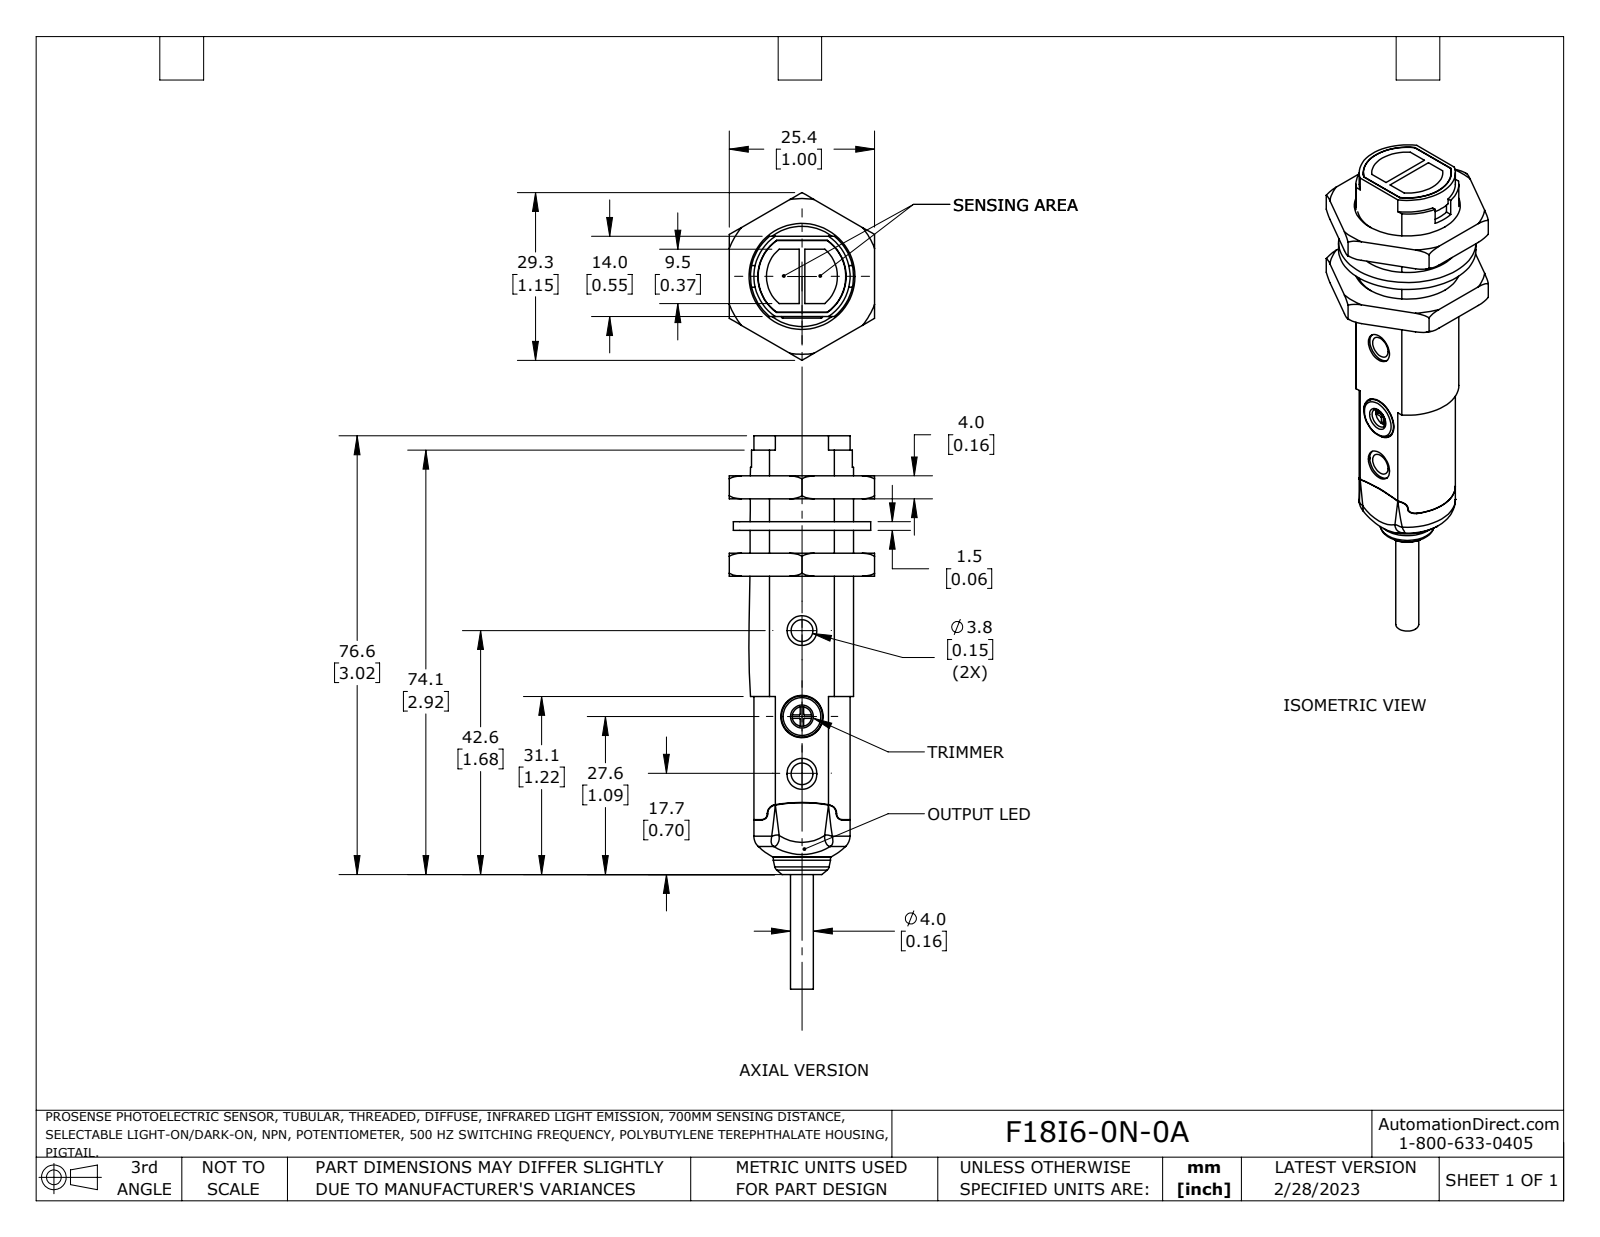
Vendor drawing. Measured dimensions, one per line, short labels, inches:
name: F18I8-BP-0A
written by: SolidWorks 2021 (AUTOMOTIVE_DESIGN)
unit: in
bodies: 4 solids, 178 faces (78 planar, 50 cylindrical, 50 other)
size: 3.802 × 1.153 × 0.998
volume: 1.134 in³; area: 12.48 in²
holes: 2× ⌀0.15, 1× ⌀0.134, 1× ⌀0.205, 1× ⌀0.291, 1× ⌀0.689, 1× ⌀0.709
bosses: 1× ⌀0.945, 1× ⌀0.394, 1× ⌀0.283, 1× ⌀0.157
rounds: 4× R0.039, 4× R0.059, 2× R0.102, 2× R1.102, 1× R0.02, 1× R0.301, 1× R0.303, 1× R0.307
face distances: 0.157, 0.374, 0.551, 0.531, 0.217, 0.315, 0.998, 0.689, 0.433, 0.059
hole spacings: 0.394, 0.591, 0.984
